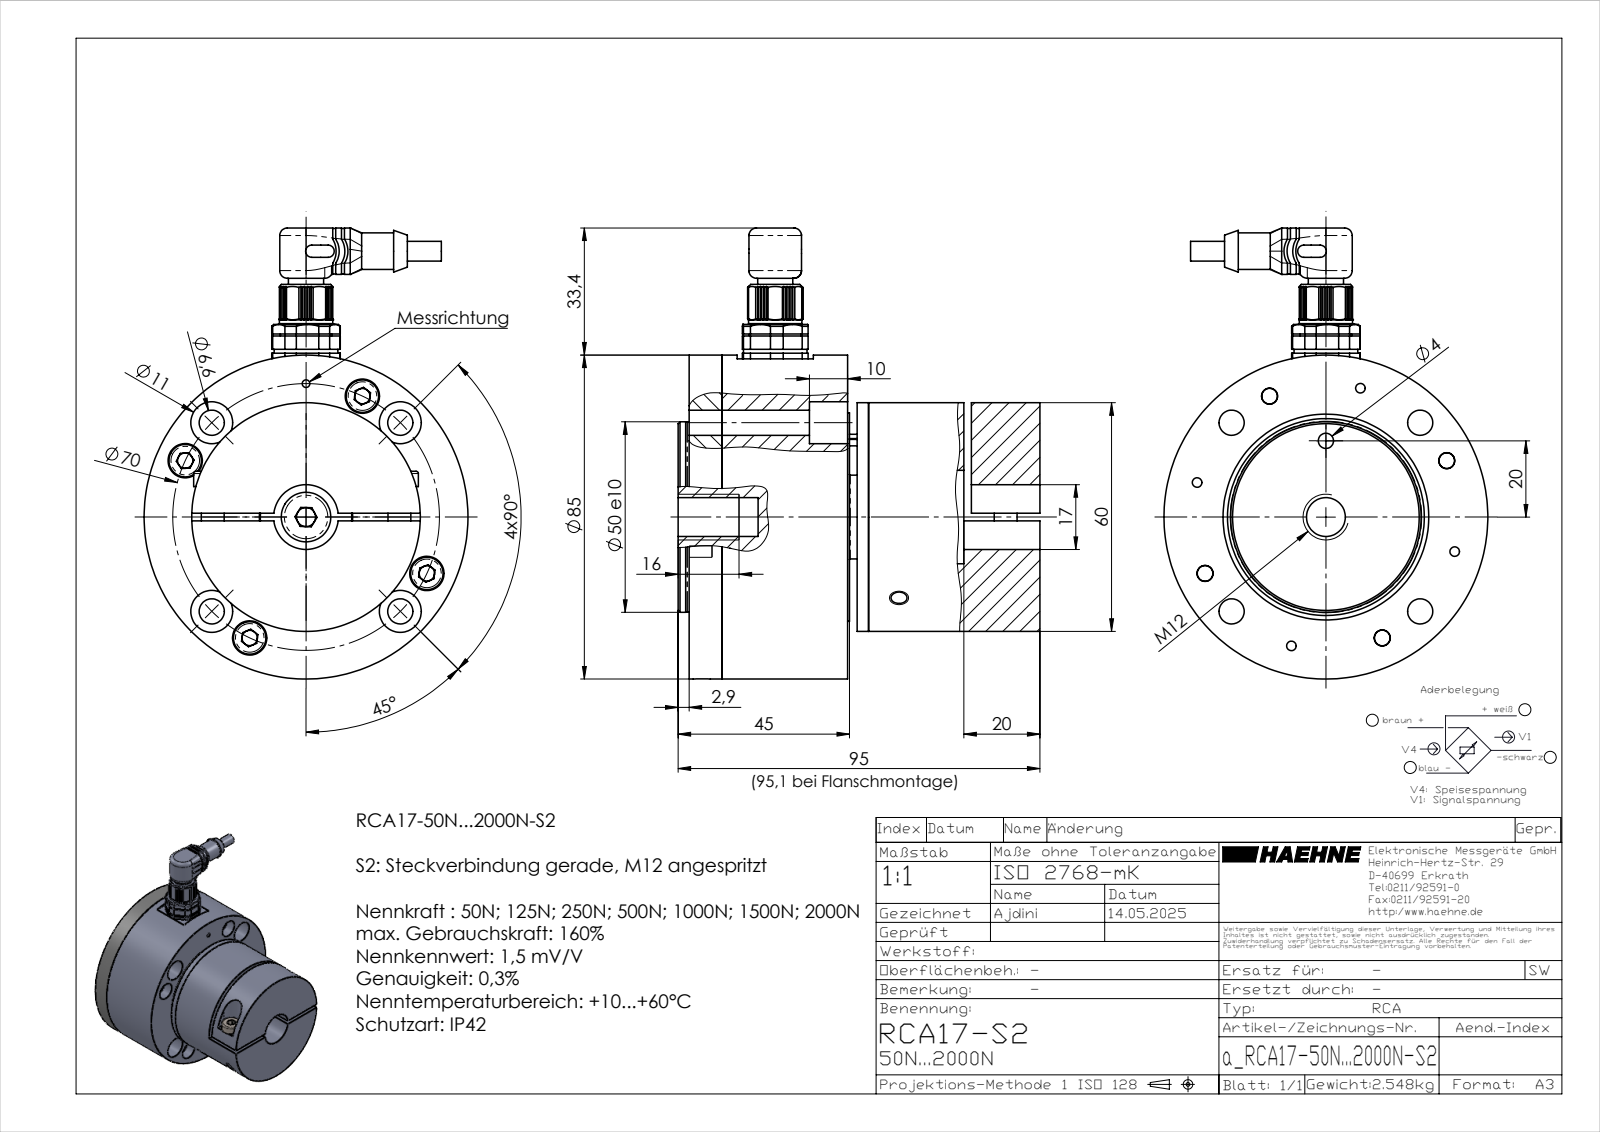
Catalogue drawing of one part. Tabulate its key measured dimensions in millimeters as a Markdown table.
| quantity | value |
| --- | --- |
| part name | inafag_1203-tvh_7zkvytp7yxkimpdvw8sj0b5w4_25; a_RC-N2 Flanschmontage Scheibe; a_RCA17-50N...2000N-S2; inafag_1203-tvh_7zkvytp7yxkimpdvw8sj0b5w4_13 (+8 more) |
| STEP written by | SolidWorks 2023 (AUTOMOTIVE_DESIGN) |
| units | millimeters |
| bodies | 53 solids, 1227 faces (663 planar, 295 cylindrical, 269 other) |
| overall size | 118.35 × 95.1 × 85 |
| volume | 370 609 mm³ |
| surface area | 112 996 mm² |
| round holes (diameter × count) | 3.4 × 9, 2.5 × 8, 6.6 × 6, 4.2 × 5, 11 × 5, 1.1 × 4, 1.15 × 4, 1.6 × 4, 1.85 × 4, 4 × 4, 5.3 × 4, 9 × 4 |
| round bosses / shafts (diameter × count) | 3 × 9, 5.7 × 8, 8.5 × 4, 5 × 4, 1.8 × 4, 1.55 × 4, 1.5 × 4, 1 × 4 |
| partial cylindrical surfaces (radius × count) | 0.2 × 16, 0.3 × 9, 0.4 × 4, 0.53 × 4, 1 × 4, 1.27 × 4, 6 × 4, 1.6 × 2 |
| main face-to-face distances | 3, 2, 8.6, 47.1, 45, 11.6, 30, 50, 35.5, 50.1 |
| hole center spacings | 35, 49.5, 24.78, 25.2, 32.8, 51.14, 56.46, 2.5 |
